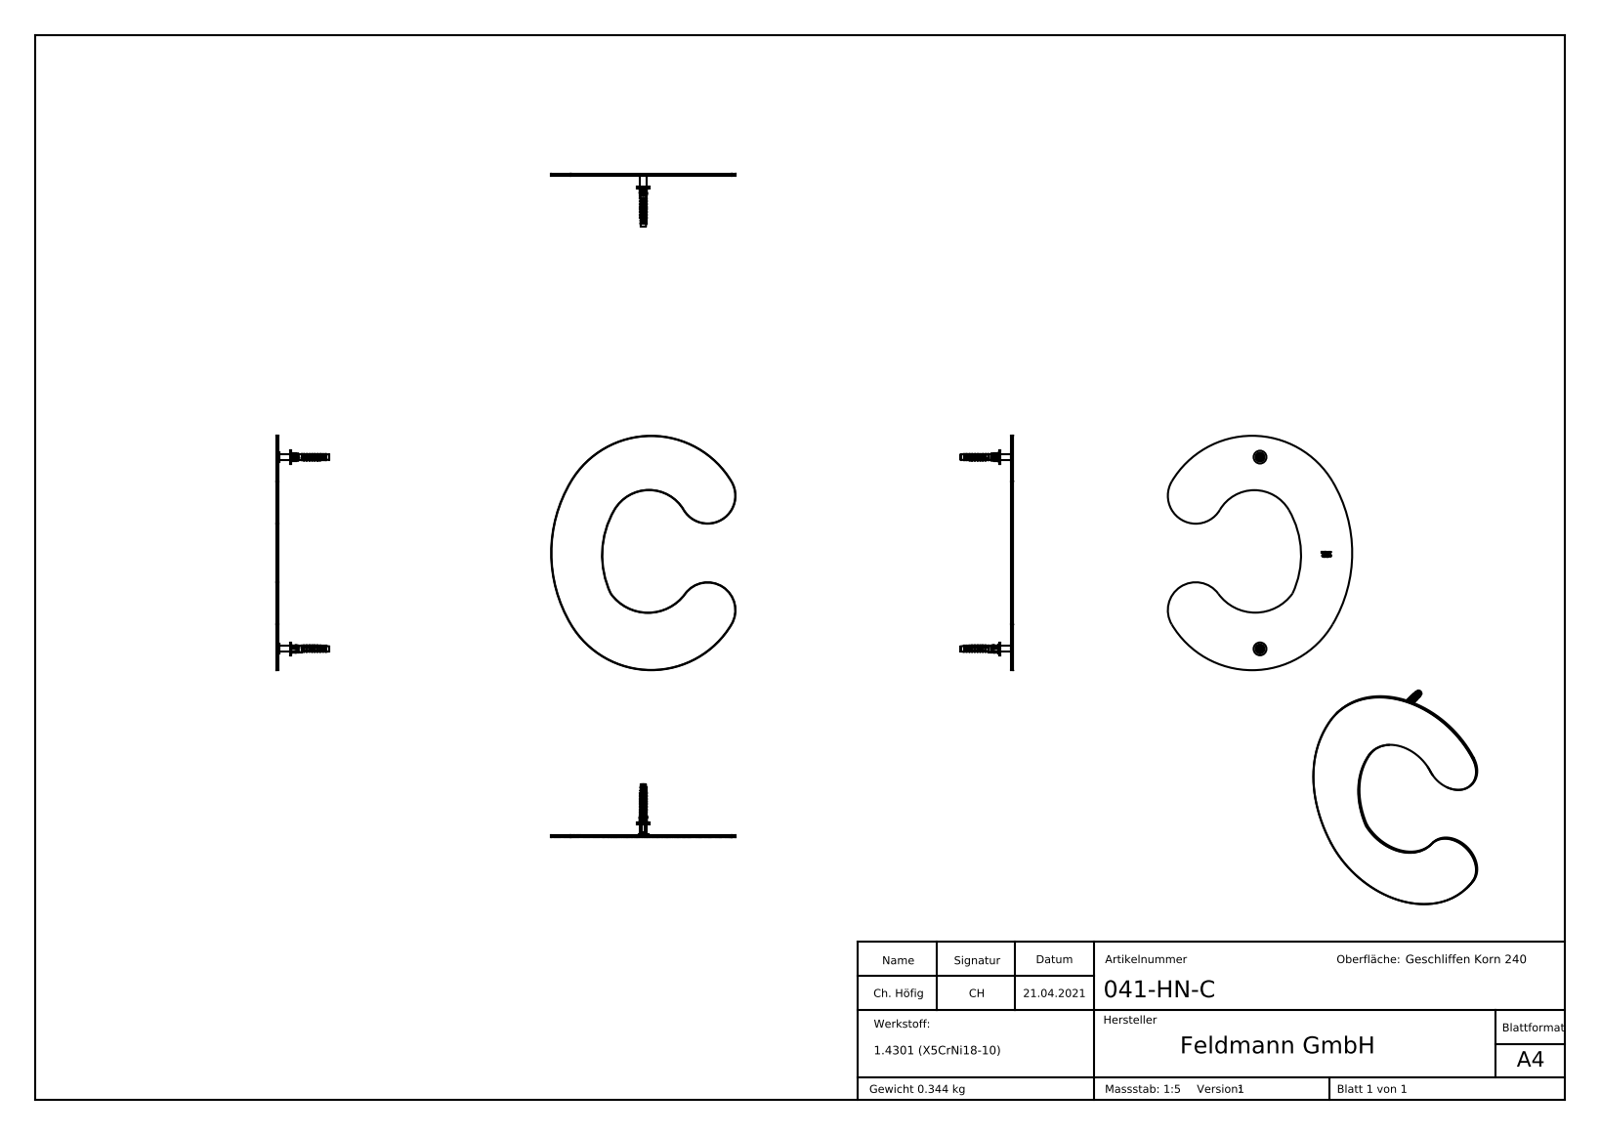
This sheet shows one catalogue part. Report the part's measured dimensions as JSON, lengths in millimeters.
{"part_name": "041-HN-X Teil3; 041-HN-X Teil4_041-HN-X Teil4; 041-HN-X Teil2_041-HN-X Teil2; 041-HN-X Teil2 (+5 more)", "step_written_by": "SolidWorks 2018 (CONFIG_CONTROL_DESIGN)", "units": "millimeters", "bodies": {"solids": 7, "faces": 1548, "planar": 358, "cylindrical": 388, "other": 802}, "overall_size": [10000, 5217.43, 4607.88], "volume_mm3": 44567, "surface_area_mm2": 48023, "round_holes": [[3.3, 2], [4.3, 2]], "round_bosses_or_shafts": [[12, 2], [9, 2], [8, 2], [6, 2], [5.8, 2], [5.6, 2], [4.6, 2], [4, 2]], "partial_cylinders_radius": [[0.1, 22], [3.5, 2], [26.2, 2], [87.77, 2], [37.56, 1], [42.91, 1], [84.68, 1], [131.27, 1]], "face_to_face_distances": [2, 11.6, 13.6, 1.1, 10.5, 12.5, 1, 0.5, 2.5, 10], "hole_center_spacings": [180]}
